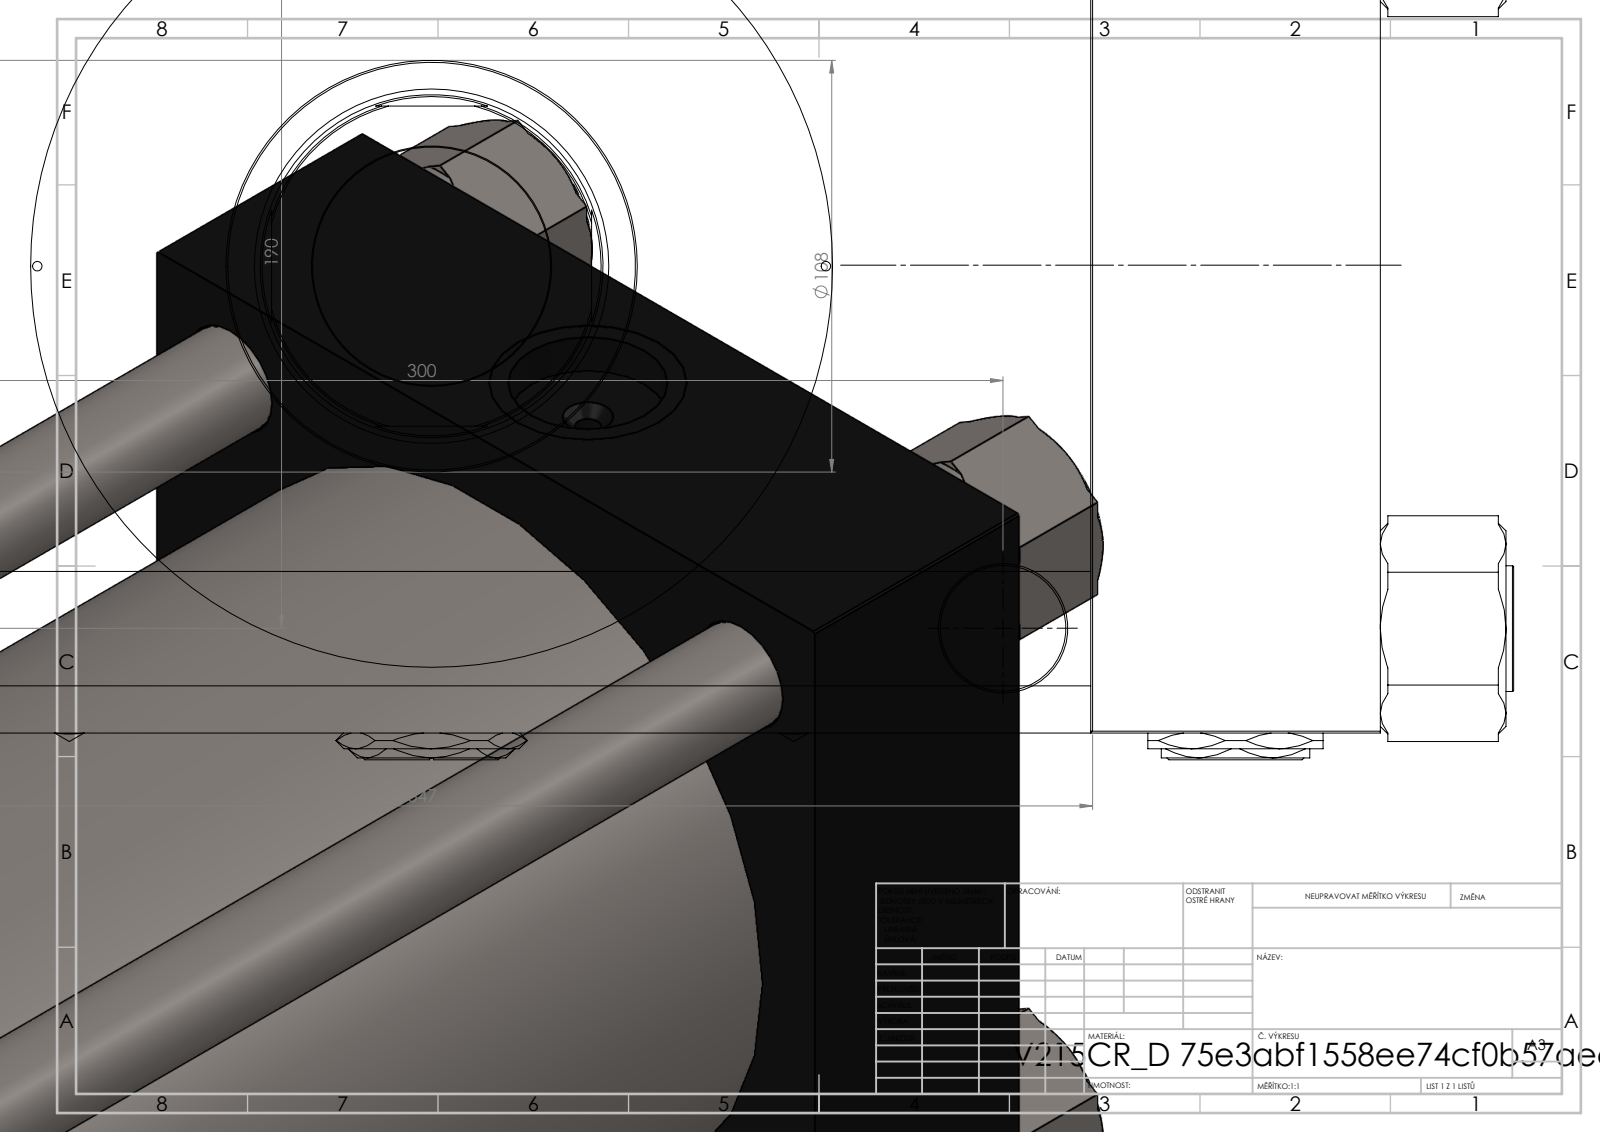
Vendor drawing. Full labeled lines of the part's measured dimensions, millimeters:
Part name (STEP PRODUCT): V215_VC_A; NUT_M5_D; Zatka_pro_OIL_PORT; V215CR_D_TYCINKA (+2 more)
STEP written by: SolidWorks 2019 (CONFIG_CONTROL_DESIGN)
Units: millimetres
Bodies: 13 solids, 1255 faces (593 planar, 102 cylindrical, 560 other)
Overall size (bounding box): 1236 × 347 × 254.22
Volume: 24 420 000 mm³ · Surface area: 2 810 000 mm²
Round holes (diameter × count): ⌀30 ×4, ⌀33 ×4, ⌀2.5 ×2, ⌀7 ×2, ⌀41.92 ×2, ⌀52 ×2, ⌀62.5 ×1, ⌀90 ×1, ⌀93 ×1, ⌀146 ×1, ⌀200 ×1, ⌀210.5 ×1
Round bosses / shafts (diameter × count): ⌀33 ×4, ⌀206 ×1, ⌀108 ×1
Partial cylindrical surfaces — rounded edges, fillets, slot ends (radius × count): R44 ×1
Main face-to-face distances: 76, 1068, 992, 245, 1144, 1125.74, 1049.74, 57.74, 18.26, 51
Hole centre spacings: 54.9, 95.47, 105.77, 134.49, 177.55, 190.2, 197.87, 220.2
